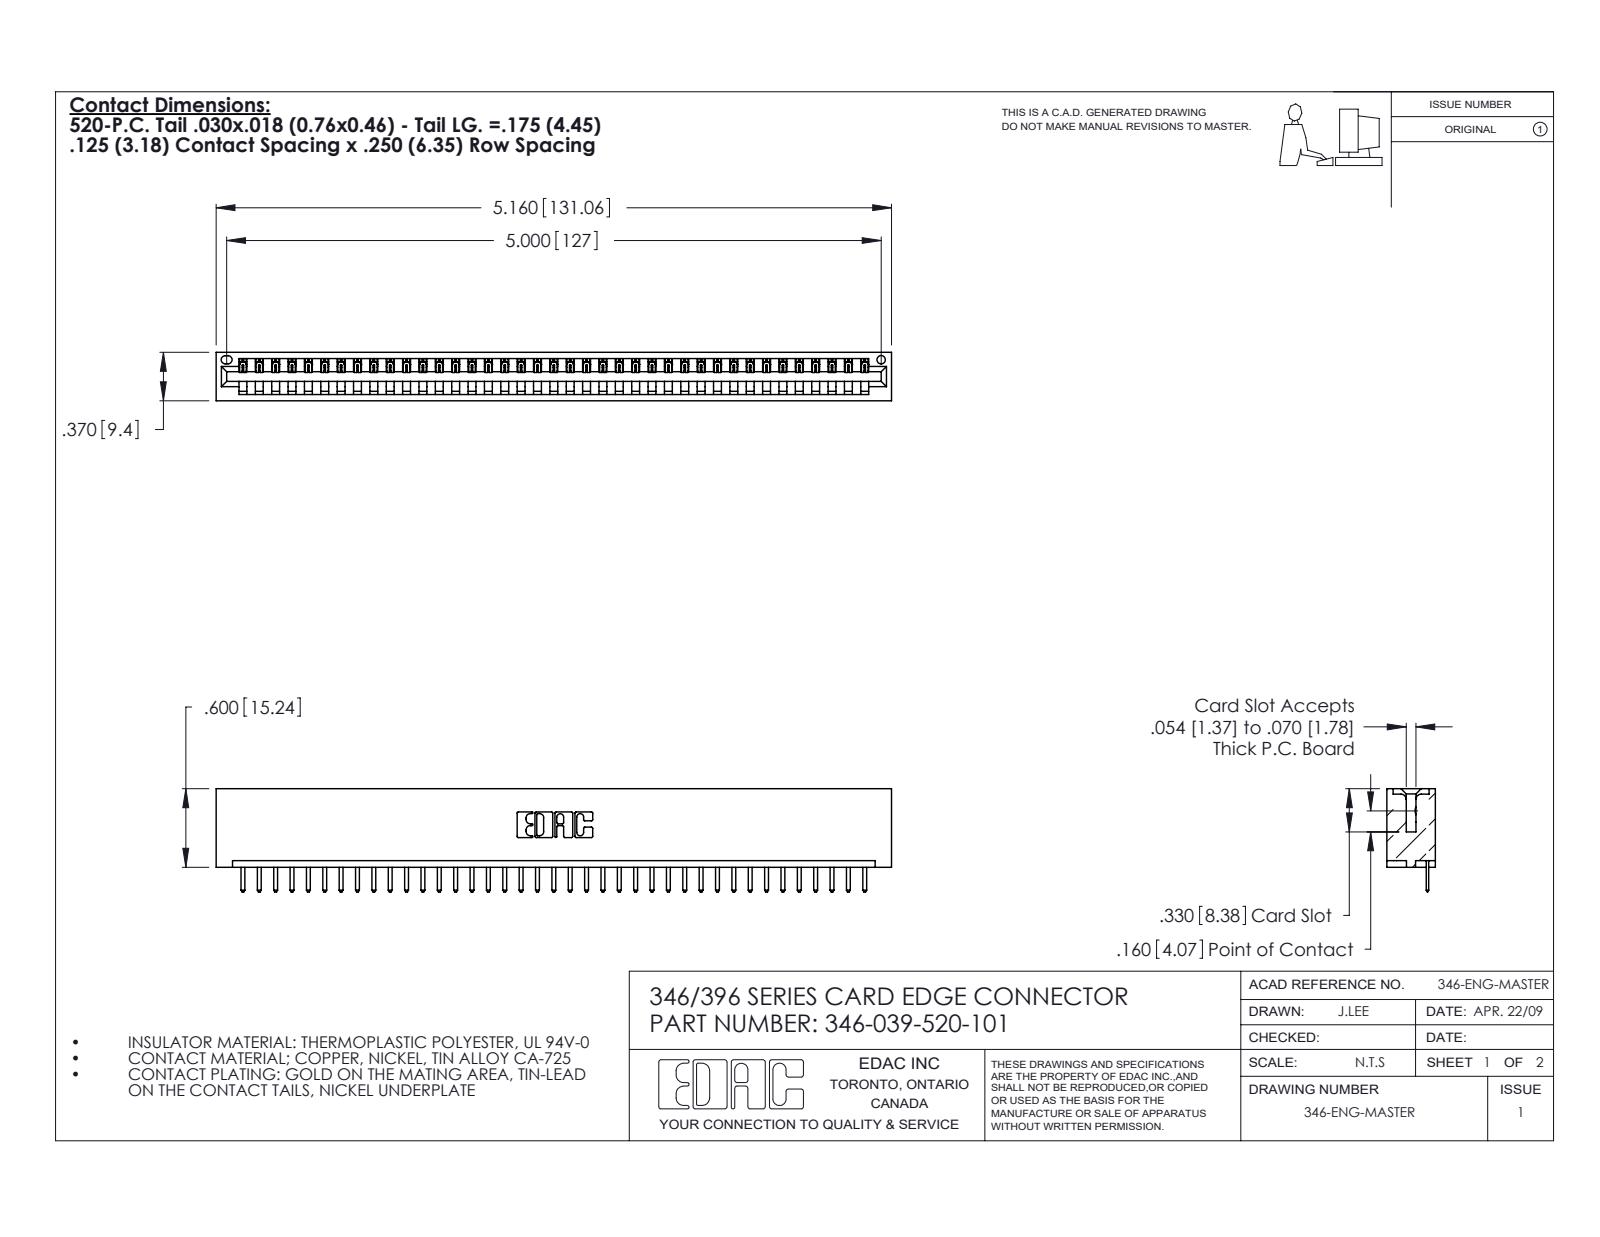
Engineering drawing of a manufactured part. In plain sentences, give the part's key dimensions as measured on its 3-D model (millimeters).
The part is named "346 Part_No Mounting Lugs; 346-039-520-101; 345-292-001_345-293-120". Its 3-D file was written by "SolidWorks 2020 (CONFIG_CONTROL_DESIGN)". It is 40 solids with 2532 faces: 1710 planar, 822 cylindrical and 0 other. Overall it measures 131.1 by 20 by 9.4 millimeters. Its volume is 13 000 cubic millimeters and its surface area 15 870 square millimeters. Round holes: 1 of diameter 1.6. Partial cylindrical surfaces (rounded edges, fillets, slot ends): 80 of radius 0.3, 78 of radius 0.2, 22 of radius 0.3, 6 of radius 0.2, 6 of radius 0.8, 3 of radius 0.7, 2 of radius 0.8, 2 of radius 1. The main face-to-face distances are 1.2, 8.2, 9.4, 6.4, 3.8, 5.6, 2.5, 4.4, 1.8, 7.6.
